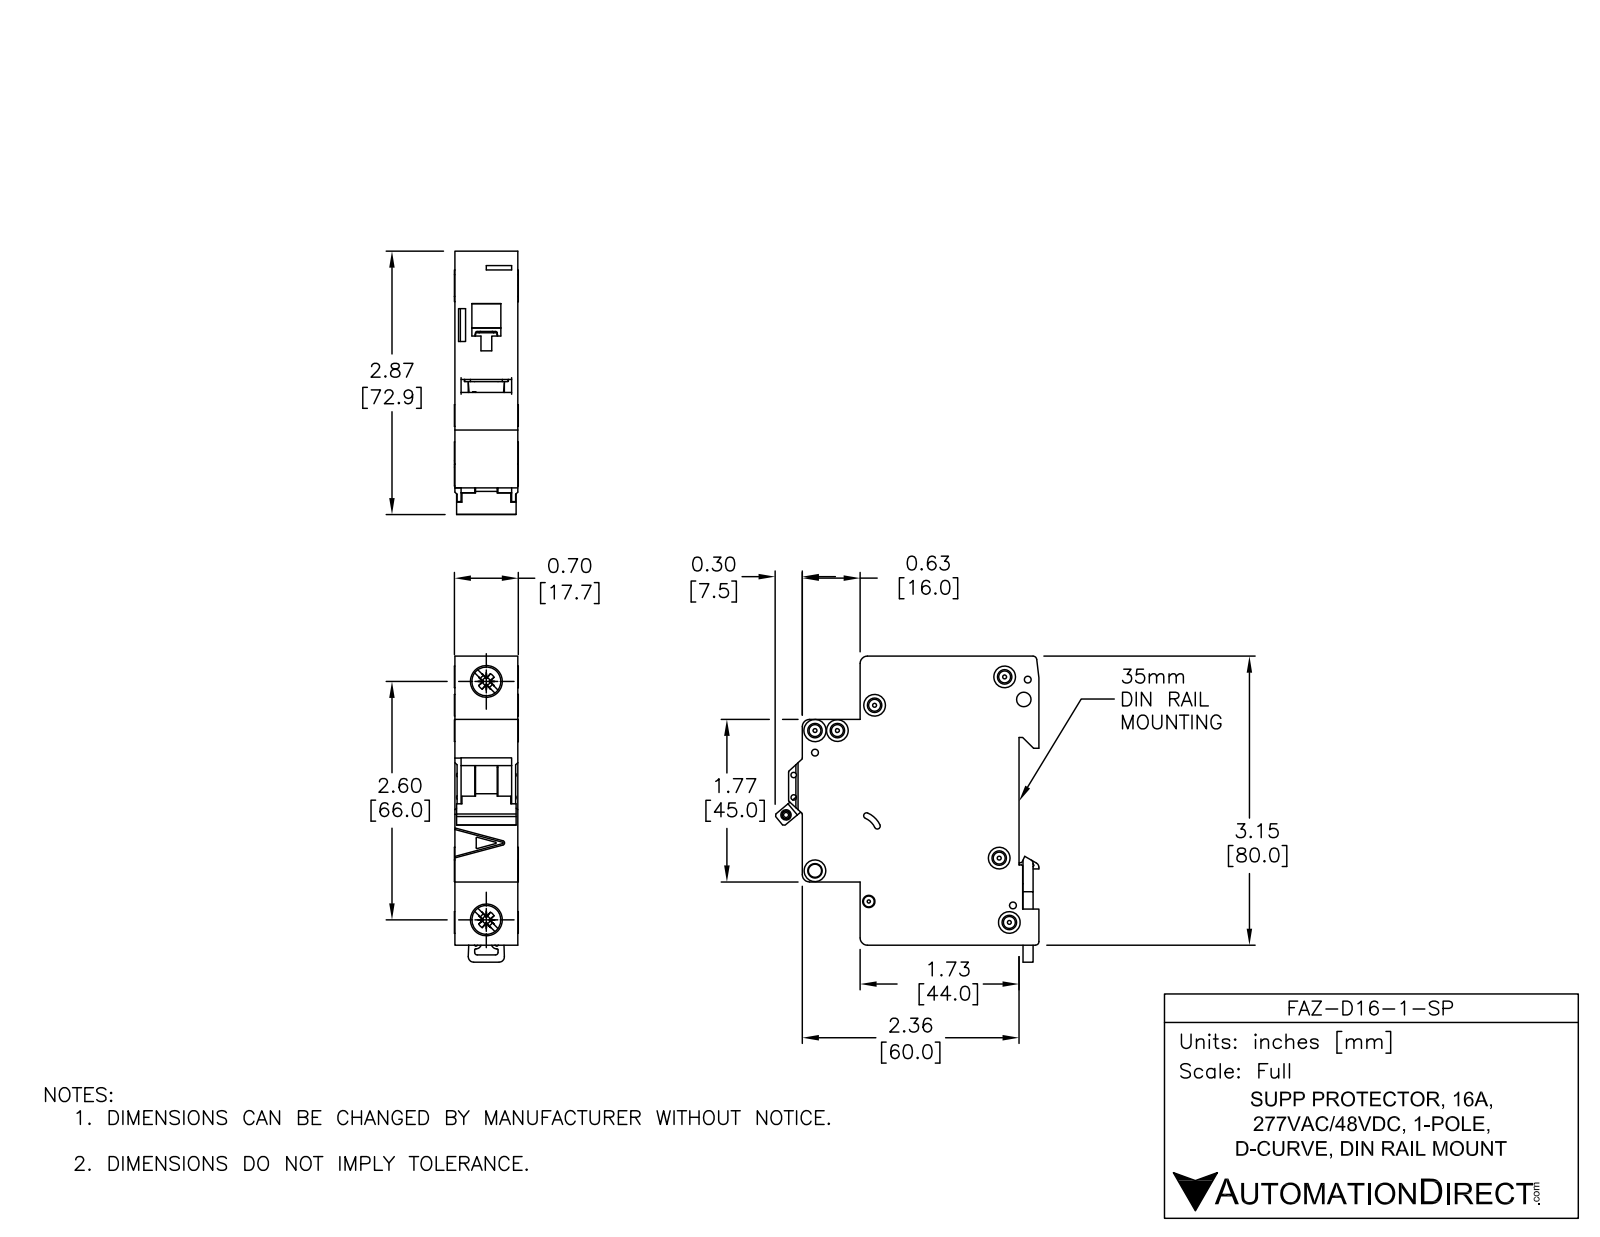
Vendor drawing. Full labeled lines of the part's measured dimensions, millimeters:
Part name (STEP PRODUCT): FAZ-D16-1-SP
STEP written by: SolidWorks 2014 (AUTOMOTIVE_DESIGN)
Units: millimetres
Bodies: 5 solids, 558 faces (235 planar, 202 cylindrical, 121 other)
Overall size (bounding box): 84.78 × 73.04 × 17.7
Volume: 74 935 mm³ · Surface area: 19 545 mm²
Round holes (diameter × count): ⌀3.6 ×6, ⌀1.9 ×3, ⌀1.09 ×2, ⌀1.5 ×2, ⌀4 ×2, ⌀7.15 ×2, ⌀2.15 ×1, ⌀2.2 ×1, ⌀2.55 ×1, ⌀3.3 ×1, ⌀3.4 ×1
Round bosses / shafts (diameter × count): ⌀6 ×4, ⌀8.2 ×2, ⌀2.5 ×1
Partial cylindrical surfaces — rounded edges, fillets, slot ends (radius × count): R0.25 ×30, R0.5 ×13, R2 ×8, R0.2 ×5, R1 ×4, R0.8 ×2, R3 ×2, R1.5 ×1
Main face-to-face distances: 17.5, 79.48, 5.5, 49.5, 44, 65.5, 60, 16, 1.75, 15.75
Hole centre spacings: 6.2, 13.64, 4.81, 5.19, 5.61, 6.1, 6.44, 8.19
